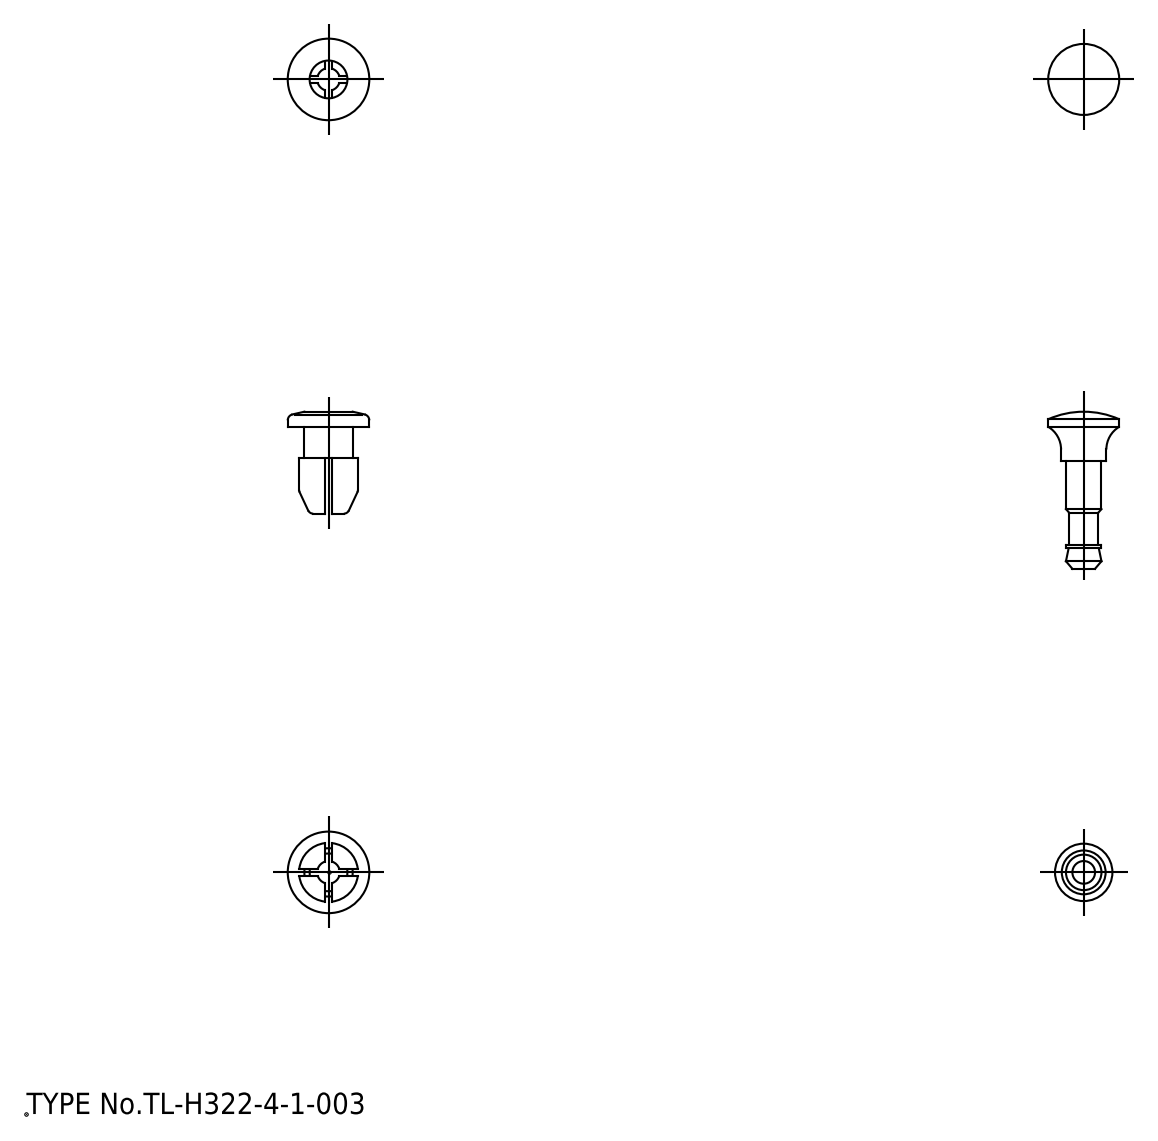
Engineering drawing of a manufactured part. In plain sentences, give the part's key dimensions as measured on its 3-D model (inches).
The part is named "grommet; plunger". Its 3-D file was written by "spGate 18.9.1 (****-****-****-****) (AUTOMOTIVE_DESIGN)". It is 2 solids with 80 faces: 26 planar, 24 cylindrical and 30 other. Overall it measures 0.898 by 0.425 by 0.425 inches. Its volume is 0.049 cubic inches and its surface area 1.742 square inches. Round holes: 1 of diameter 0.197. Round bosses or shafts: 1 of diameter 0.425, 1 of diameter 0.37, 1 of diameter 0.307, 1 of diameter 0.252, 1 of diameter 0.236, 1 of diameter 0.185, 1 of diameter 0.15. Partial cylindrical surfaces (rounded edges, fillets, slot ends): 1 of radius 0.059. The main face-to-face distances are 0.039, 0.079, 0.161, 0.24, 0.35, 0.189, 0.11, 0.453, 0.106, 0.213.
